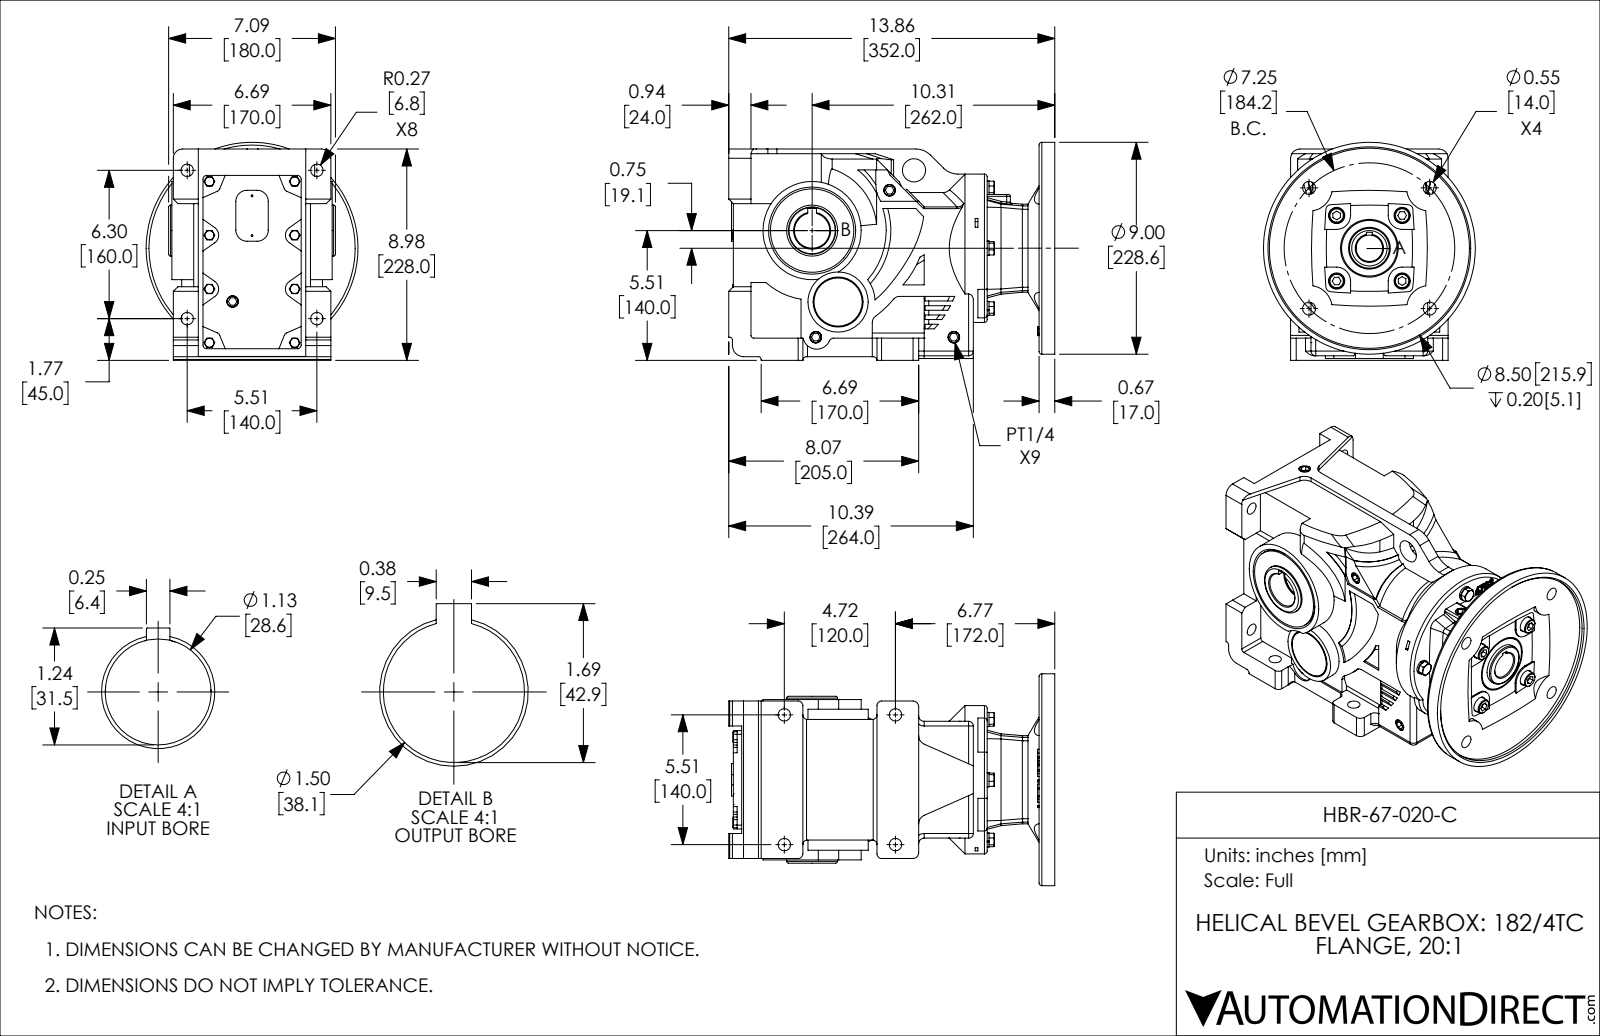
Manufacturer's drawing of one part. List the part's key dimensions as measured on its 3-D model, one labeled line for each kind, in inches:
Part name (STEP PRODUCT): HBR-67-020-C
STEP written by: SolidWorks 2018 (AUTOMOTIVE_DESIGN)
Units: inches
Bodies: 1 solid, 1100 faces (560 planar, 258 cylindrical, 282 other)
Overall size (bounding box): 13.858 × 9.262 × 9
Volume: 513.2 in³ · Surface area: 714.3 in²
Round holes (diameter × count): ⌀0.531 ×8, ⌀0.323 ×4, ⌀0.354 ×4, ⌀0.551 ×4, ⌀0.689 ×4, ⌀0.079 ×2, ⌀0.984 ×1, ⌀1.125 ×1, ⌀1.417 ×1, ⌀1.5 ×1, ⌀1.575 ×1, ⌀8.5 ×1
Round bosses / shafts (diameter × count): ⌀0.63 ×4, ⌀0.606 ×4, ⌀0.315 ×4, ⌀9 ×1, ⌀6.299 ×1, ⌀4.173 ×1, ⌀3.543 ×1, ⌀2.559 ×1
Partial cylindrical surfaces — rounded edges, fillets, slot ends (radius × count): R0.197 ×20, R0.157 ×12, R0.394 ×11, R0.079 ×7, R0.472 ×5, R0.591 ×5, R0.236 ×4, R0.689 ×4
Main face-to-face distances: 0.197, 0.079, 0.469, 0.945, 0.059, 13.461, 12.992, 8.78, 4.961, 0.118
Hole centre spacings: 2.563, 5.728, 1.656, 1.817, 2.559, 3.619, 4.125, 4.125
